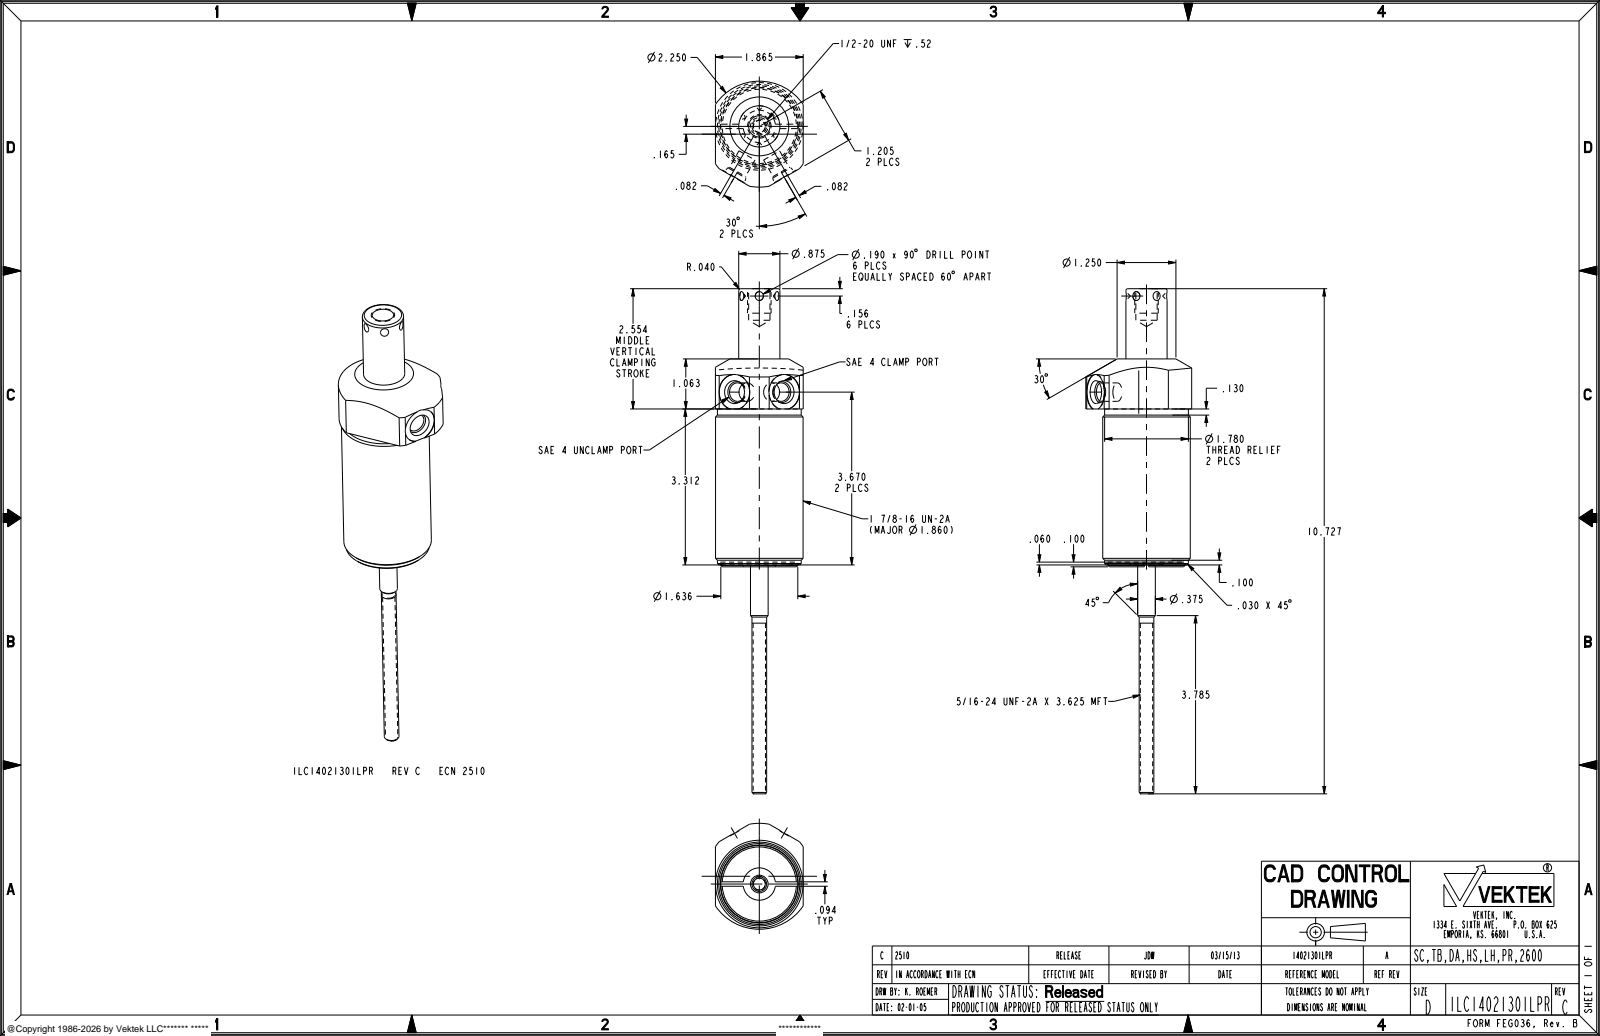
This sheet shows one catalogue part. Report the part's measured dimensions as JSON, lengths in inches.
{"part_name": "ILC14021301LPR", "step_written_by": "PRO/ENGINEER BY PARAMETRIC TECHNOLOGY CORPORATION, 2007460 (AUTOMOTIVE_DESIGN_CC2)", "units": "inches", "bodies": {"solids": 1, "faces": 103, "planar": 29, "cylindrical": 36, "other": 38}, "overall_size": [10.727, 2.25, 1.865], "volume_in3": 13.48, "surface_area_in2": 48.6, "round_holes": [[0.392, 2], [0.75, 2], [0.453, 1], [0.687, 1], [1.656, 1]], "round_bosses_or_shafts": [[1.86, 1], [1.78, 1], [1.636, 1], [0.875, 1], [0.5, 1], [0.375, 1], [0.312, 1], [0.262, 1]], "partial_cylinders_radius": [[1.125, 1]], "face_to_face_distances": [3.352, 1.865, 4.415, 1.063, 0.06, 3.292, 4.355, 5.906, 5.846, 2.554]}
